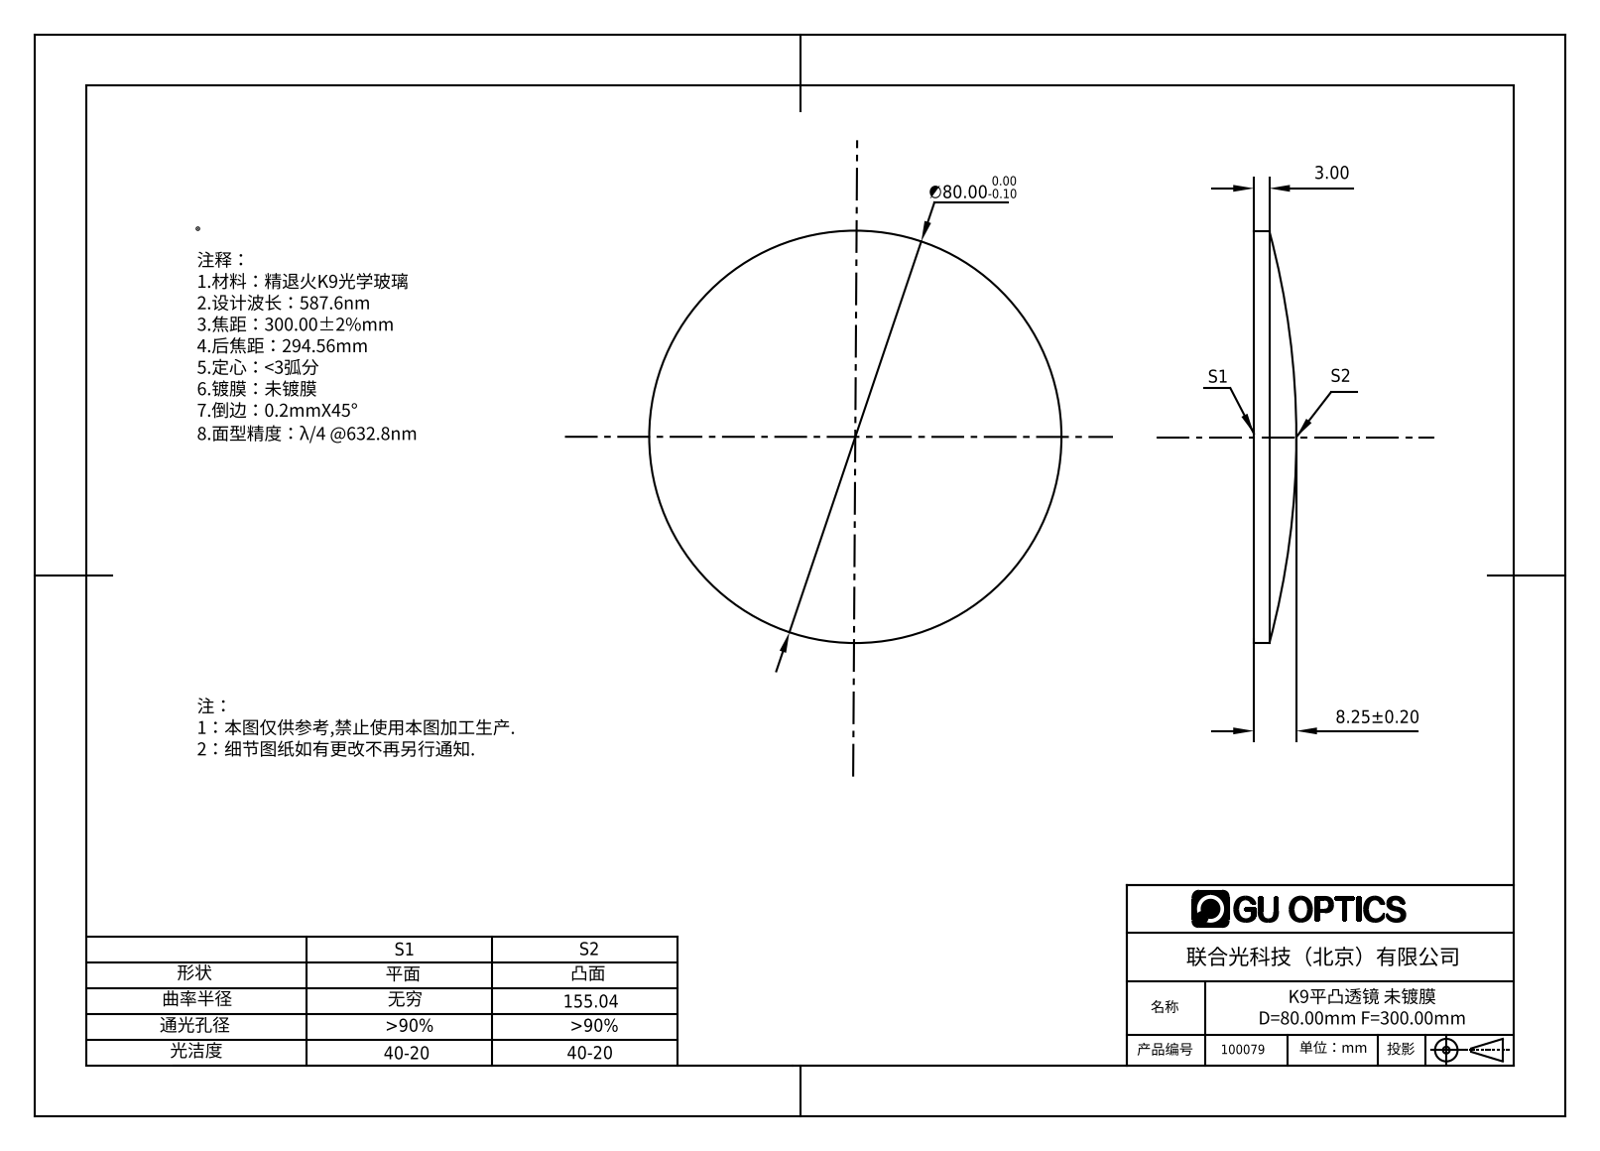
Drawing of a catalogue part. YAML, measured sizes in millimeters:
part_name: "100079"
step_written_by: "SolidWorks 2016 (AUTOMOTIVE_DESIGN)"
units: millimeters
bodies: {solids: 1, faces: 5, planar: 1, cylindrical: 2, other: 2}
overall_size: [80, 80, 8.25]
volume: 28351
surface_area: 10894
round_bosses_or_shafts:
  - {diameter: 80, count: 1}
